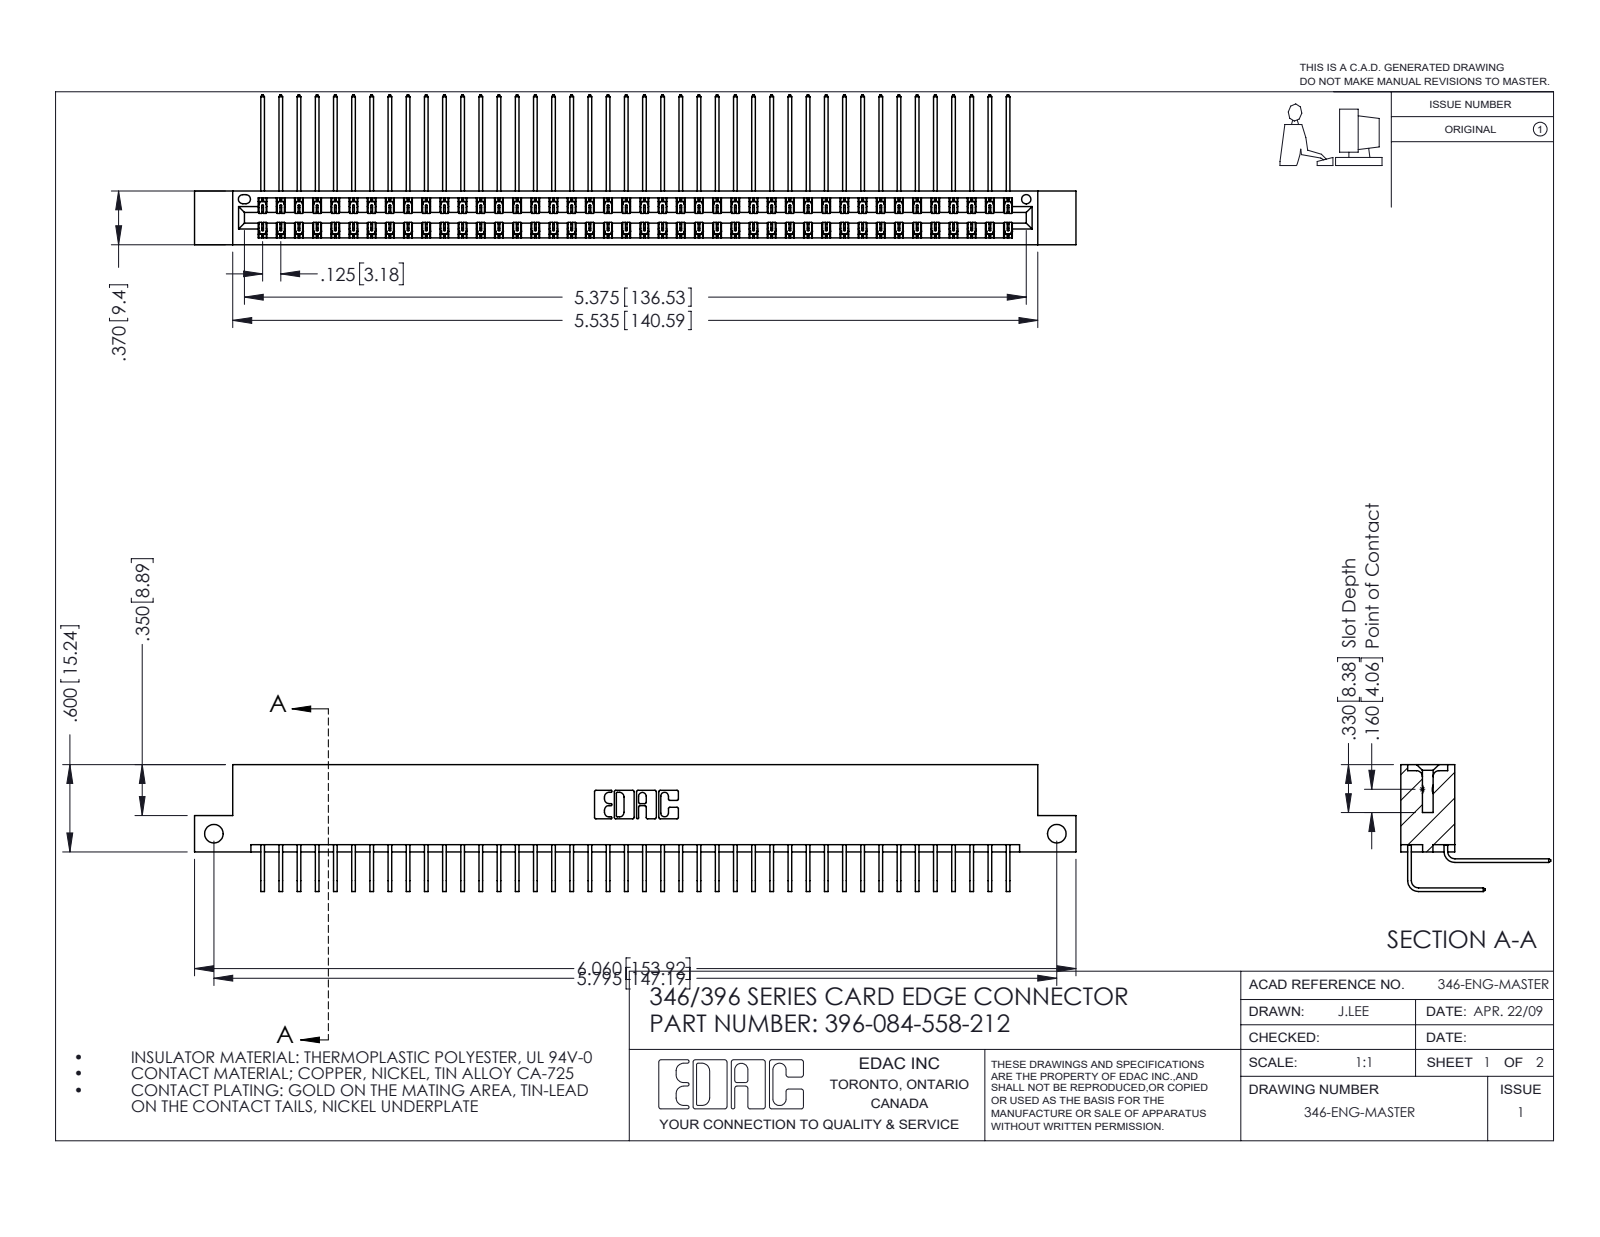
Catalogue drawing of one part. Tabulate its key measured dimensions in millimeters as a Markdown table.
| quantity | value |
| --- | --- |
| part name | 396-084-558-212; 345-292-001_558 Tail - 2; 346 Part_Flush Mounting Lugs - Side Mount; 345-292-001_558 559 Tail - 1 |
| STEP written by | SolidWorks 2016 (CONFIG_CONTROL_DESIGN) |
| units | millimeters |
| bodies | 85 solids, 4658 faces (3184 planar, 1474 cylindrical, 0 other) |
| overall size | 153.9 × 26.2 × 22.2 |
| volume | 15 400 mm³ |
| surface area | 23 370 mm² |
| round holes (diameter × count) | 3.3 × 2, 1.6 × 1 |
| partial cylindrical surfaces (radius × count) | 0.2 × 126, 0.3 × 22, 0.2 × 6, 0.8 × 6, 0.7 × 3, 0.4 × 2, 0.6 × 2, 0.6 × 2 |
| main face-to-face distances | 8.2, 1.2, 0.6, 6.4, 9.4, 7.6, 1.8, 7, 3.8, 5.6 |
| hole center spacings | 147.2 |
